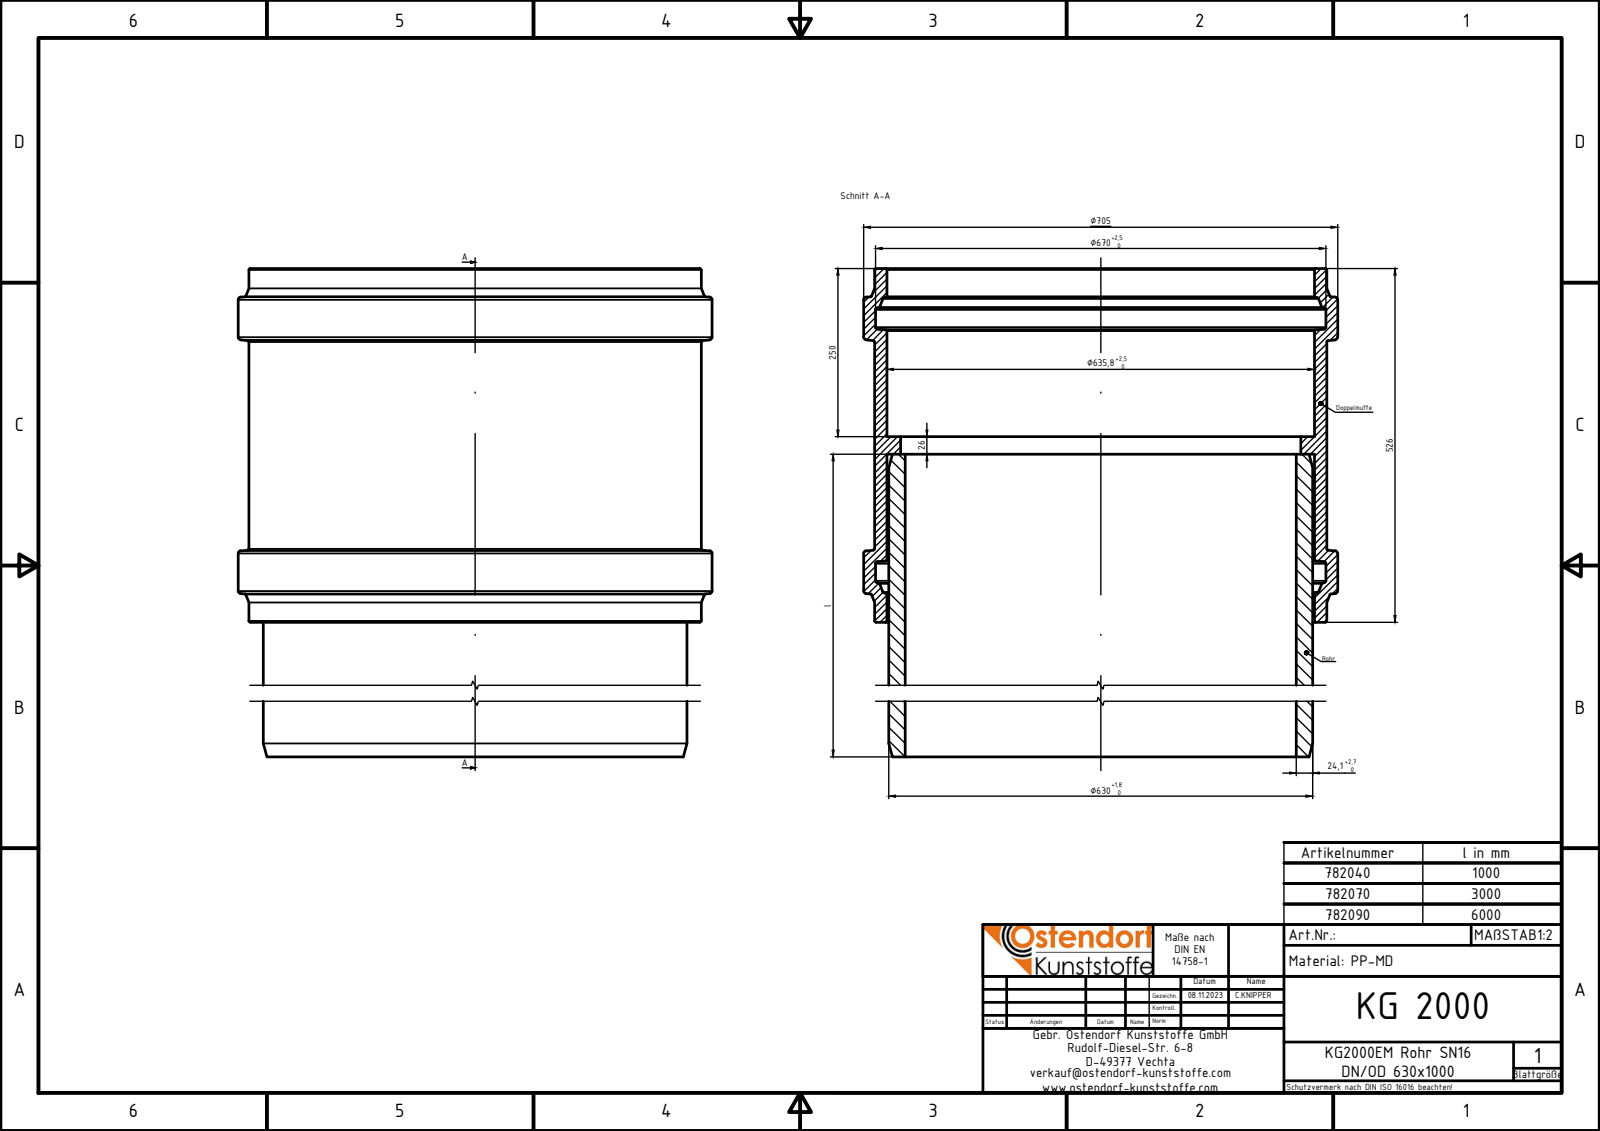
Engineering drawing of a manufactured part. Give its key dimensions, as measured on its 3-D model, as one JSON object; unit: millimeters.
{"part_name": "782040z", "step_written_by": "Autodesk Inventor 2024 (AUTOMOTIVE_DESIGN)", "units": "millimeters", "bodies": {"solids": 1, "faces": 60, "planar": 6, "cylindrical": 14, "other": 40}, "overall_size": [1276, 704.8, 704.8], "volume_mm3": 68410000, "surface_area_mm2": 6353000, "round_holes": [[581.8, 1], [594.8, 1], [635.8, 1], [670, 1]], "round_bosses_or_shafts": [[704.8, 1], [672.6, 1], [630, 1]], "face_to_face_distances": [276, 250, 1026, 750, 1276, 526, 1000, 26]}
